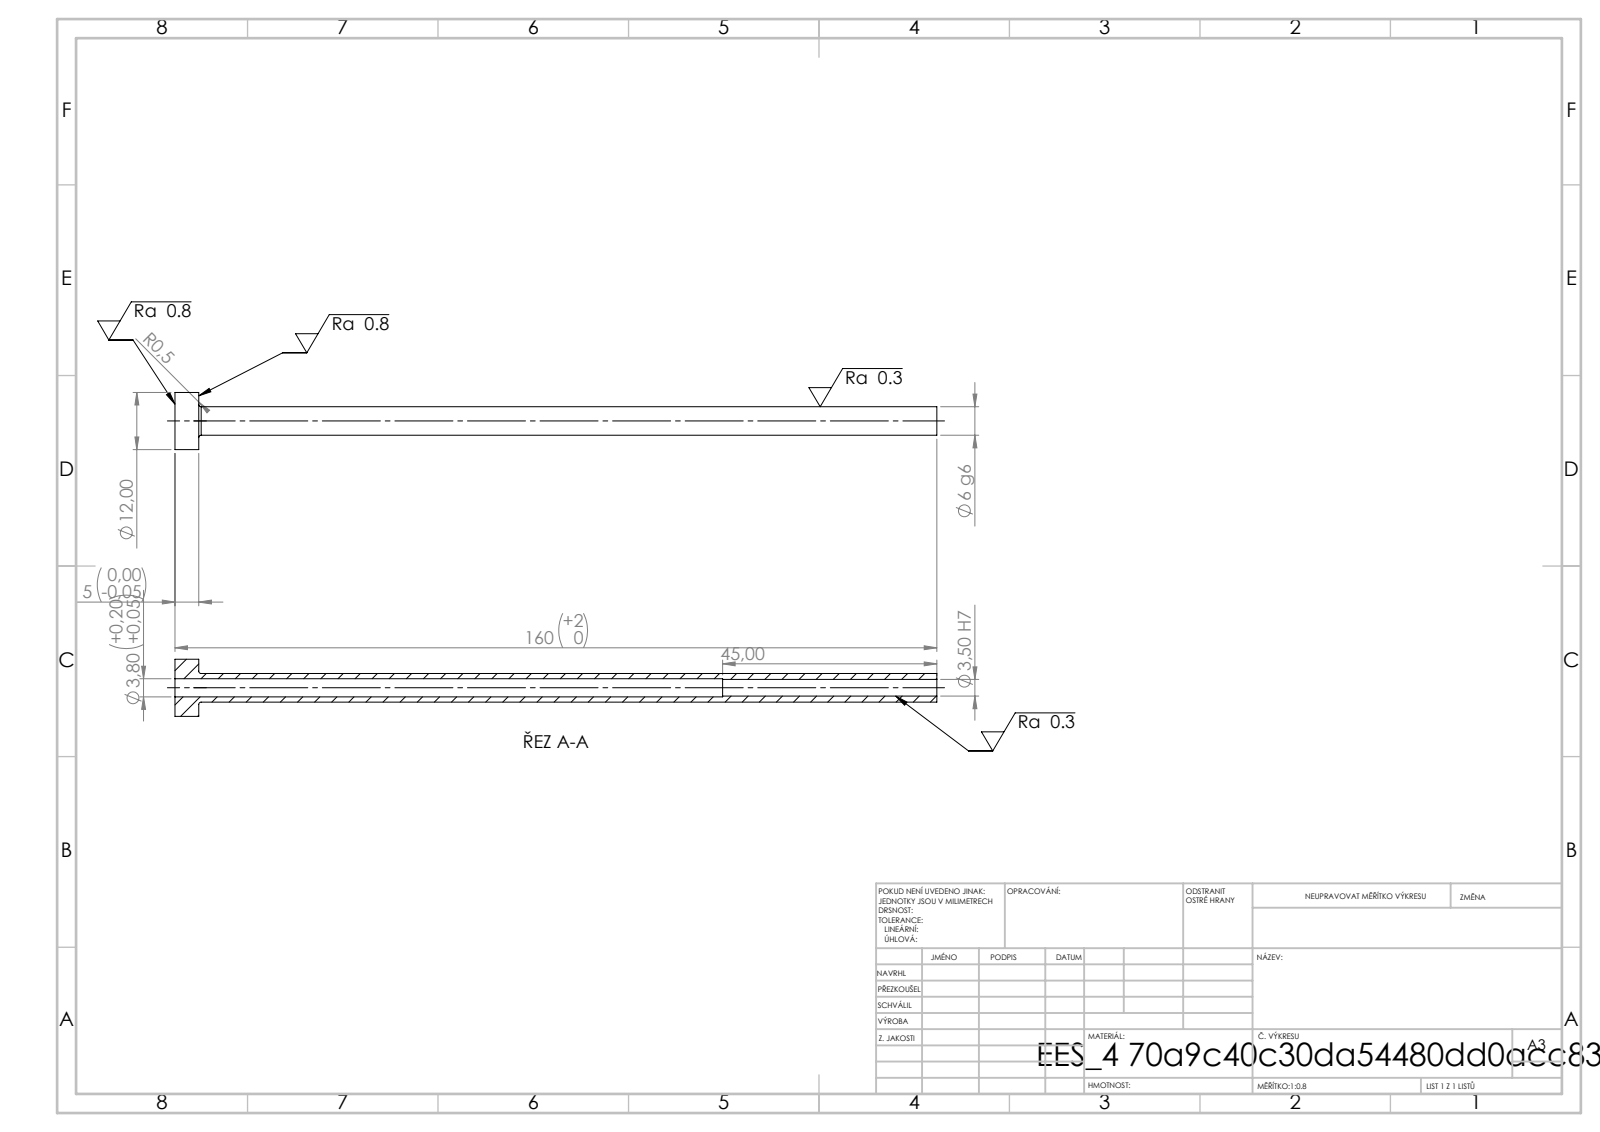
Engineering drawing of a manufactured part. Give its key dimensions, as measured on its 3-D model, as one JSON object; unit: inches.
{"step_written_by": "SolidWorks 2019 (CONFIG_CONTROL_DESIGN)", "units": "inches", "bodies": {"solids": 1, "faces": 14, "planar": 4, "cylindrical": 8, "other": 2}, "overall_size": [6.299, 0.472, 0.472], "volume_in3": 0.196, "surface_area_in2": 8.031, "round_holes": [[0.138, 1], [0.15, 1]], "round_bosses_or_shafts": [[0.472, 1], [0.236, 1]], "face_to_face_distances": [0.197, 6.299, 6.102, 4.528, 4.331, 1.772]}
